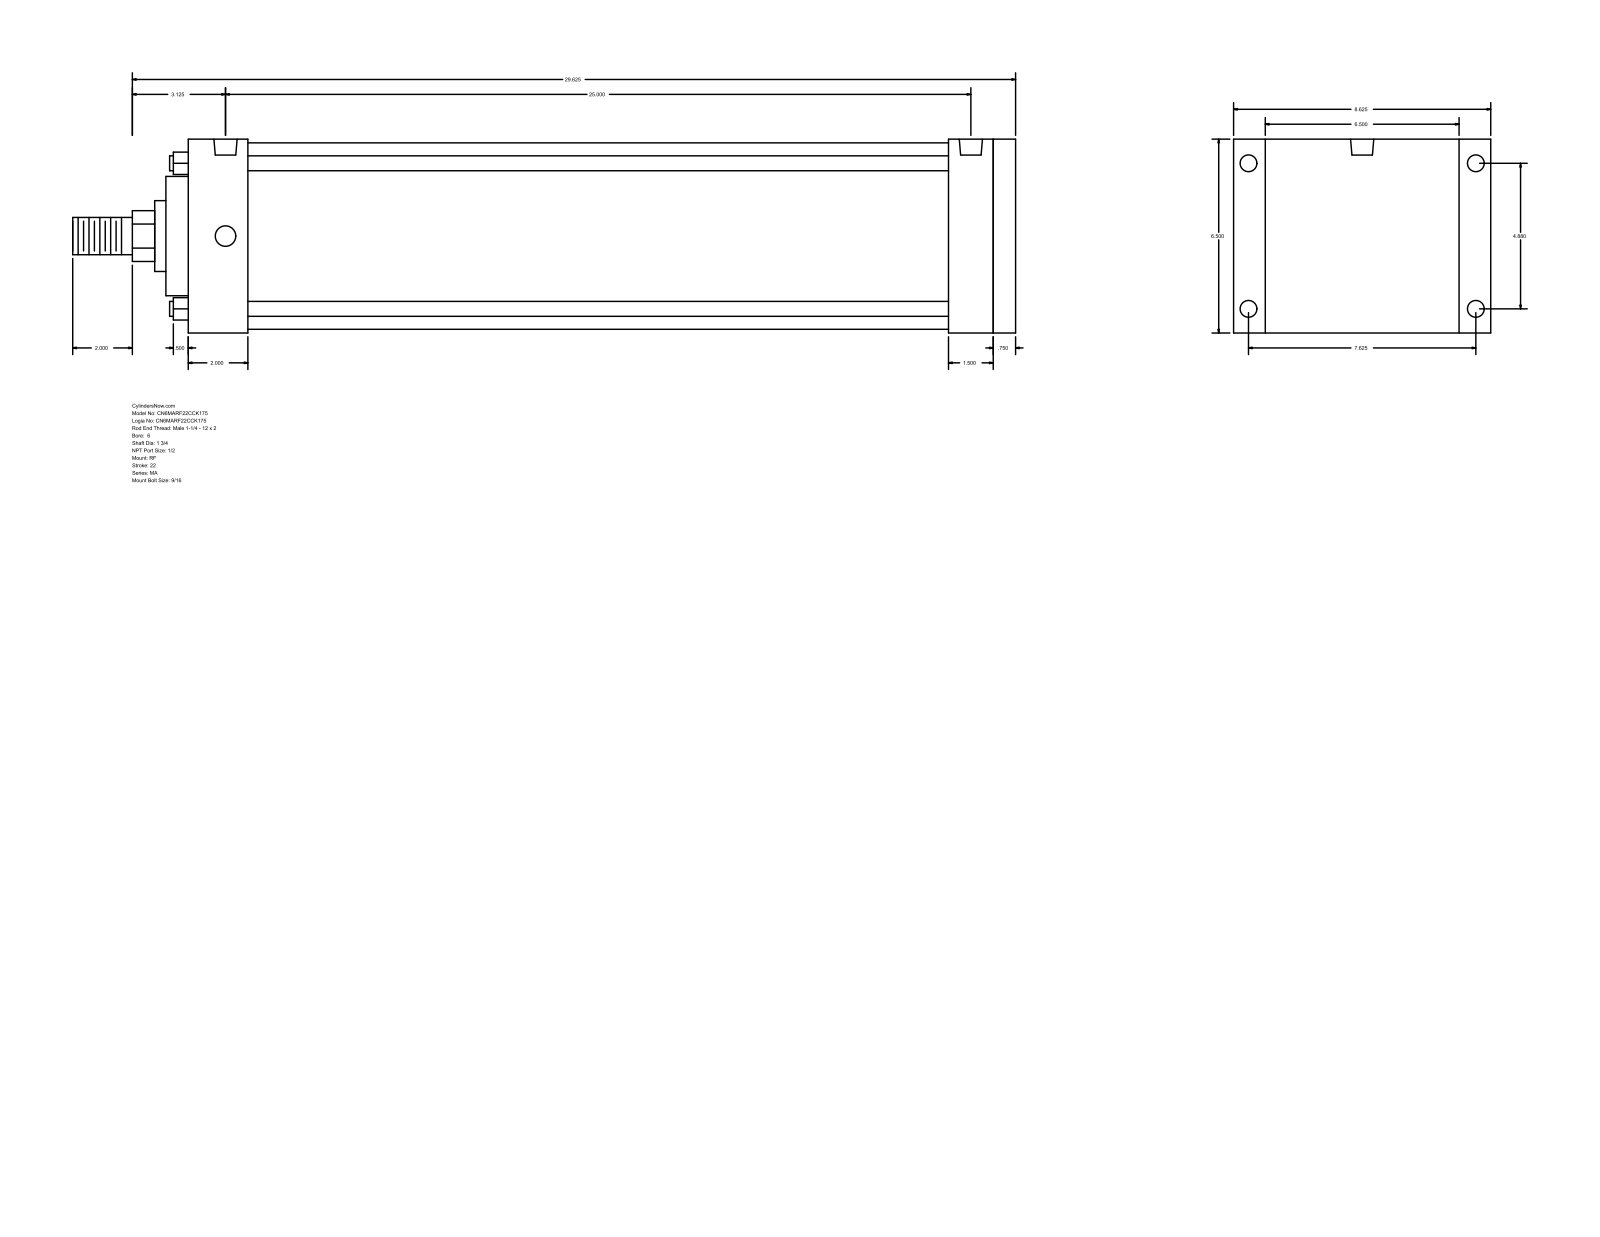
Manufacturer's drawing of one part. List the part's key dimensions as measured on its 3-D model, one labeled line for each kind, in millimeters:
Part name (STEP PRODUCT): MA_RF__0600_1.75
STEP written by: GSSL Pune (CONFIG_CONTROL_DESIGN)
Units: millimetres
Bodies: 0 solids, 94 faces (65 planar, 29 cylindrical, 0 other)
Overall size (bounding box): 803.27 × 219.07 × 165.1
Round holes (diameter × count): ⌀14.29 ×4, ⌀17.46 ×4, ⌀19.77 ×2
Round bosses / shafts (diameter × count): ⌀12.7 ×4, ⌀158.75 ×1, ⌀101.6 ×1, ⌀60.33 ×1, ⌀44.45 ×1, ⌀31.75 ×1
Partial cylindrical surfaces — rounded edges, fillets, slot ends (radius × count): R21.63 ×1
Main face-to-face distances: 165.1, 704.86, 685.8, 19.06, 50.8, 19.05, 635, 654.06, 647.71, 596.91
Hole centre spacings: 123.96, 193.68, 229.95, 635
